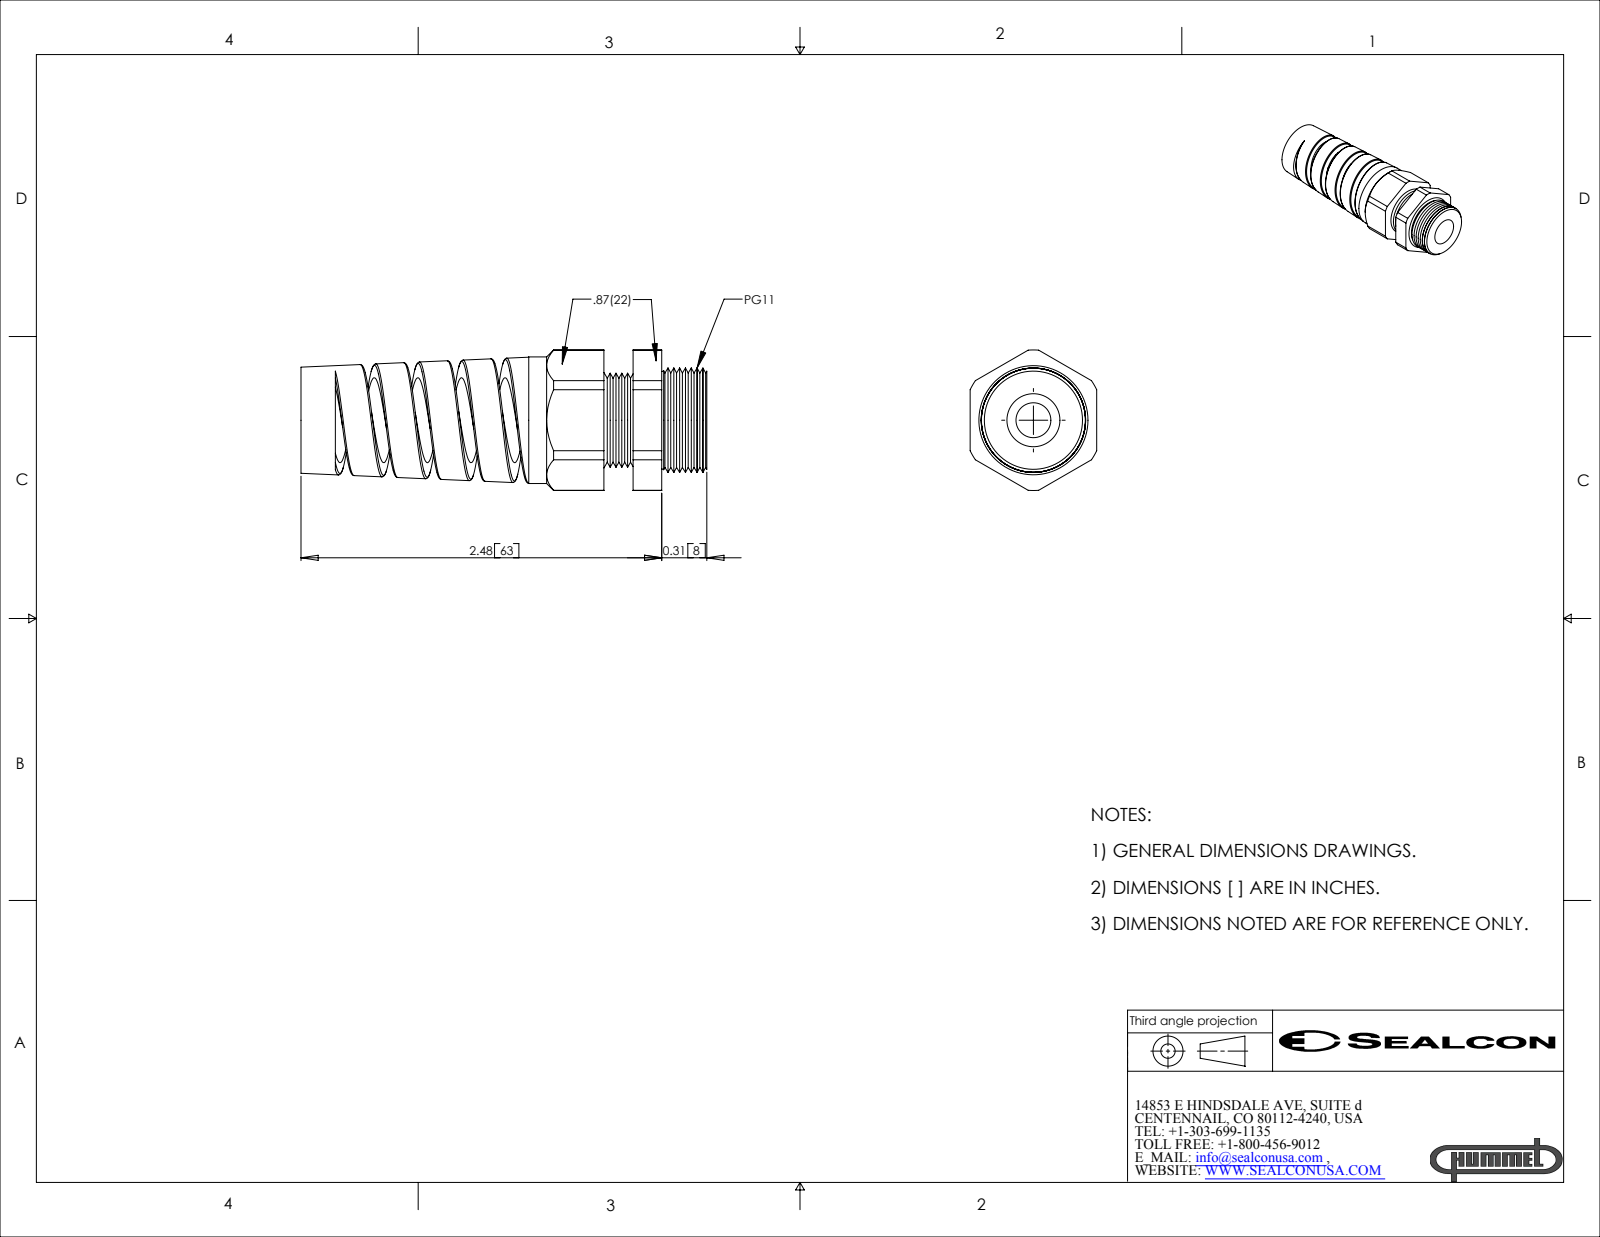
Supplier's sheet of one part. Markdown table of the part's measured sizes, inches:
| quantity | value |
| --- | --- |
| part name | CF11BR-BK |
| STEP written by | SolidWorks 2007 (CONFIG_CONTROL_DESIGN) |
| units | inches |
| bodies | 2 solids, 146 faces (24 planar, 35 cylindrical, 87 other) |
| overall size | 2.79 × 0.966 × 0.87 |
| volume | 0.81 in³ |
| surface area | 16.32 in² |
| round holes (diameter × count) | 0.24 × 1, 0.584 × 1, 0.657 × 1 |
| round bosses / shafts (diameter × count) | 0.87 × 1 |
| partial cylindrical surfaces (radius × count) | 0.302 × 1, 0.483 × 1 |
| main face-to-face distances | 0.87, 0.201, 0.707, 0.507, 0.398, 0.197, 0.31, 0.443, 0.643, 0.84 |
